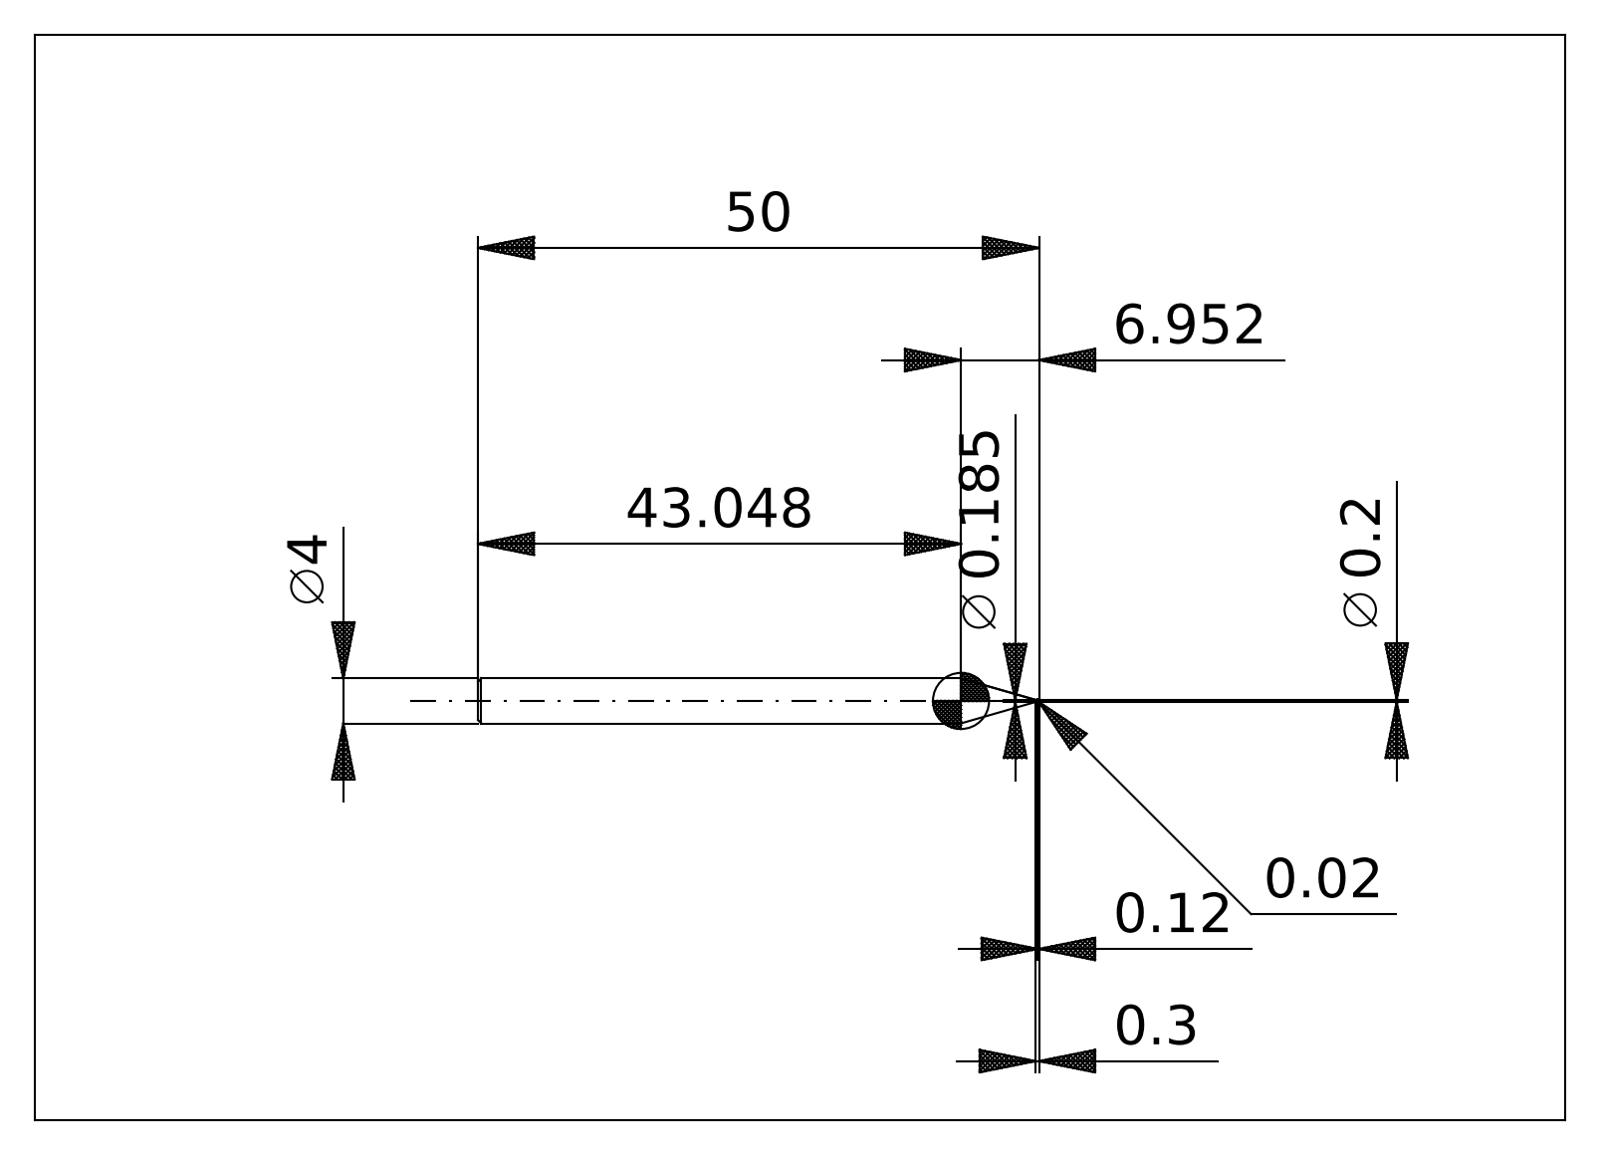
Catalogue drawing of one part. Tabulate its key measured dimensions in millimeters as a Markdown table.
| quantity | value |
| --- | --- |
| STEP written by | ACIS (automotive_design) |
| units | millimeters |
| bodies | 2 solids, 26 faces (6 planar, 8 cylindrical, 12 other) |
| overall size | 50 × 4 × 4 |
| volume | 570 mm³ |
| surface area | 597 mm² |
| round bosses / shafts (diameter × count) | 4 × 1 |
| main face-to-face distances | 50, 49.97, 49.88, 6.95, 6.92, 6.83, 43.05 |
